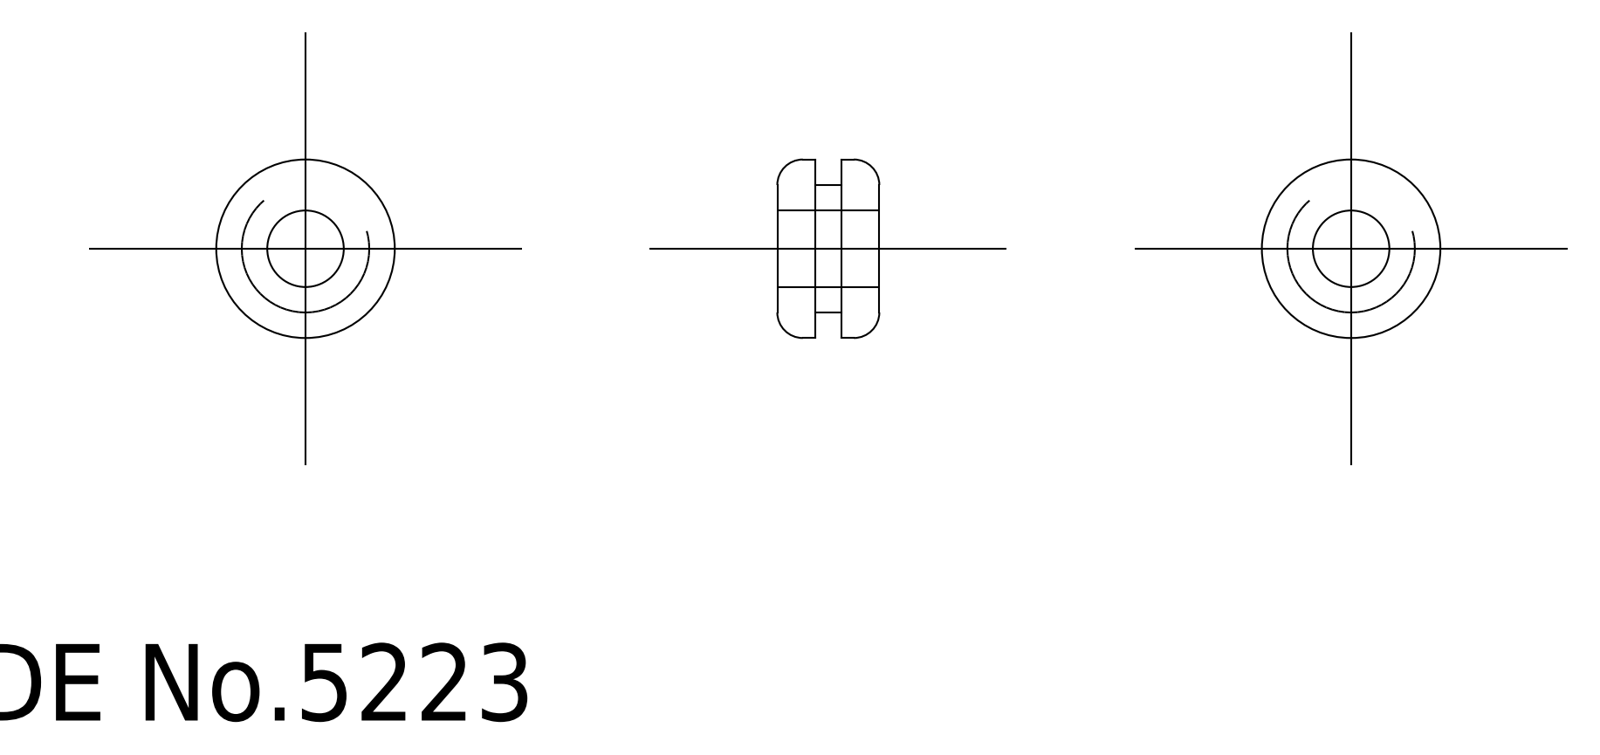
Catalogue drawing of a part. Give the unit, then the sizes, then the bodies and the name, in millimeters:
Units: millimetres
Overall size (bounding box): 7 × 7 × 4
Volume: 98 mm³ · Surface area: 200 mm²
Bodies: 1 solid, 16 faces (0 planar, 0 cylindrical, 16 other)
Part name (STEP PRODUCT): grommet
STEP written by: CADfix (AUTOMOTIVE_DESIGN)
